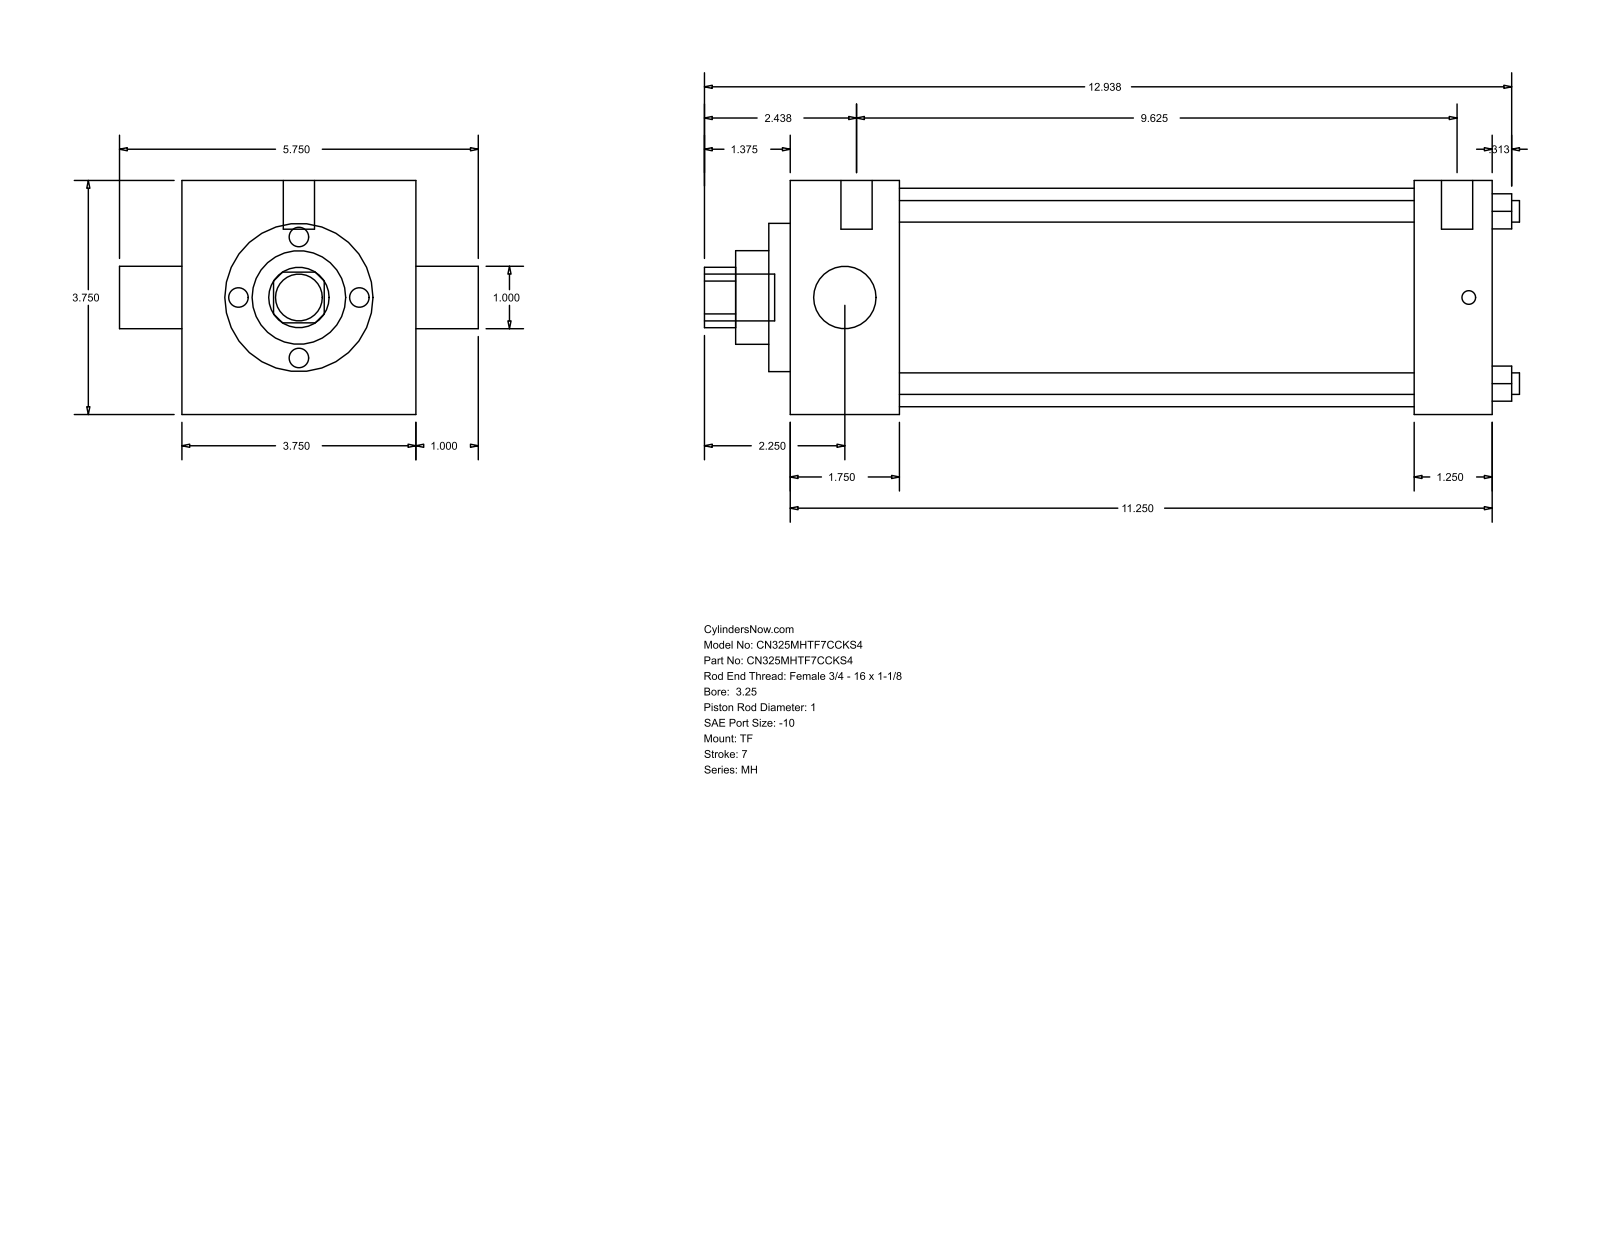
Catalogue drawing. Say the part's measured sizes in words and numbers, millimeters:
The part is named "MH_TF__0325_1". Its 3-D file was written by "GSSL Pune (CONFIG_CONTROL_DESIGN)". It is 0 solids with 86 faces: 61 planar, 25 cylindrical and 0 other. Overall it measures 331.79 by 146.05 by 95.25 millimeters. Round holes: 4 of diameter 8.76, 2 of diameter 25.4, 1 of diameter 38.1, 1 of diameter 60.33, 1 of diameter 88.9. Round bosses or shafts: 3 of diameter 5.56, 2 of diameter 12.7, 1 of diameter 19.05. Partial cylindrical surfaces (rounded edges, fillets, slot ends): 1 of radius 12.29. The main face-to-face distances are 95.24, 285.76, 44.46, 254.01, 209.55, 241.3, 31.75, 8.73, 53.19, 262.74. The hole center spacings are 49.57, 70.1, 99.14.
